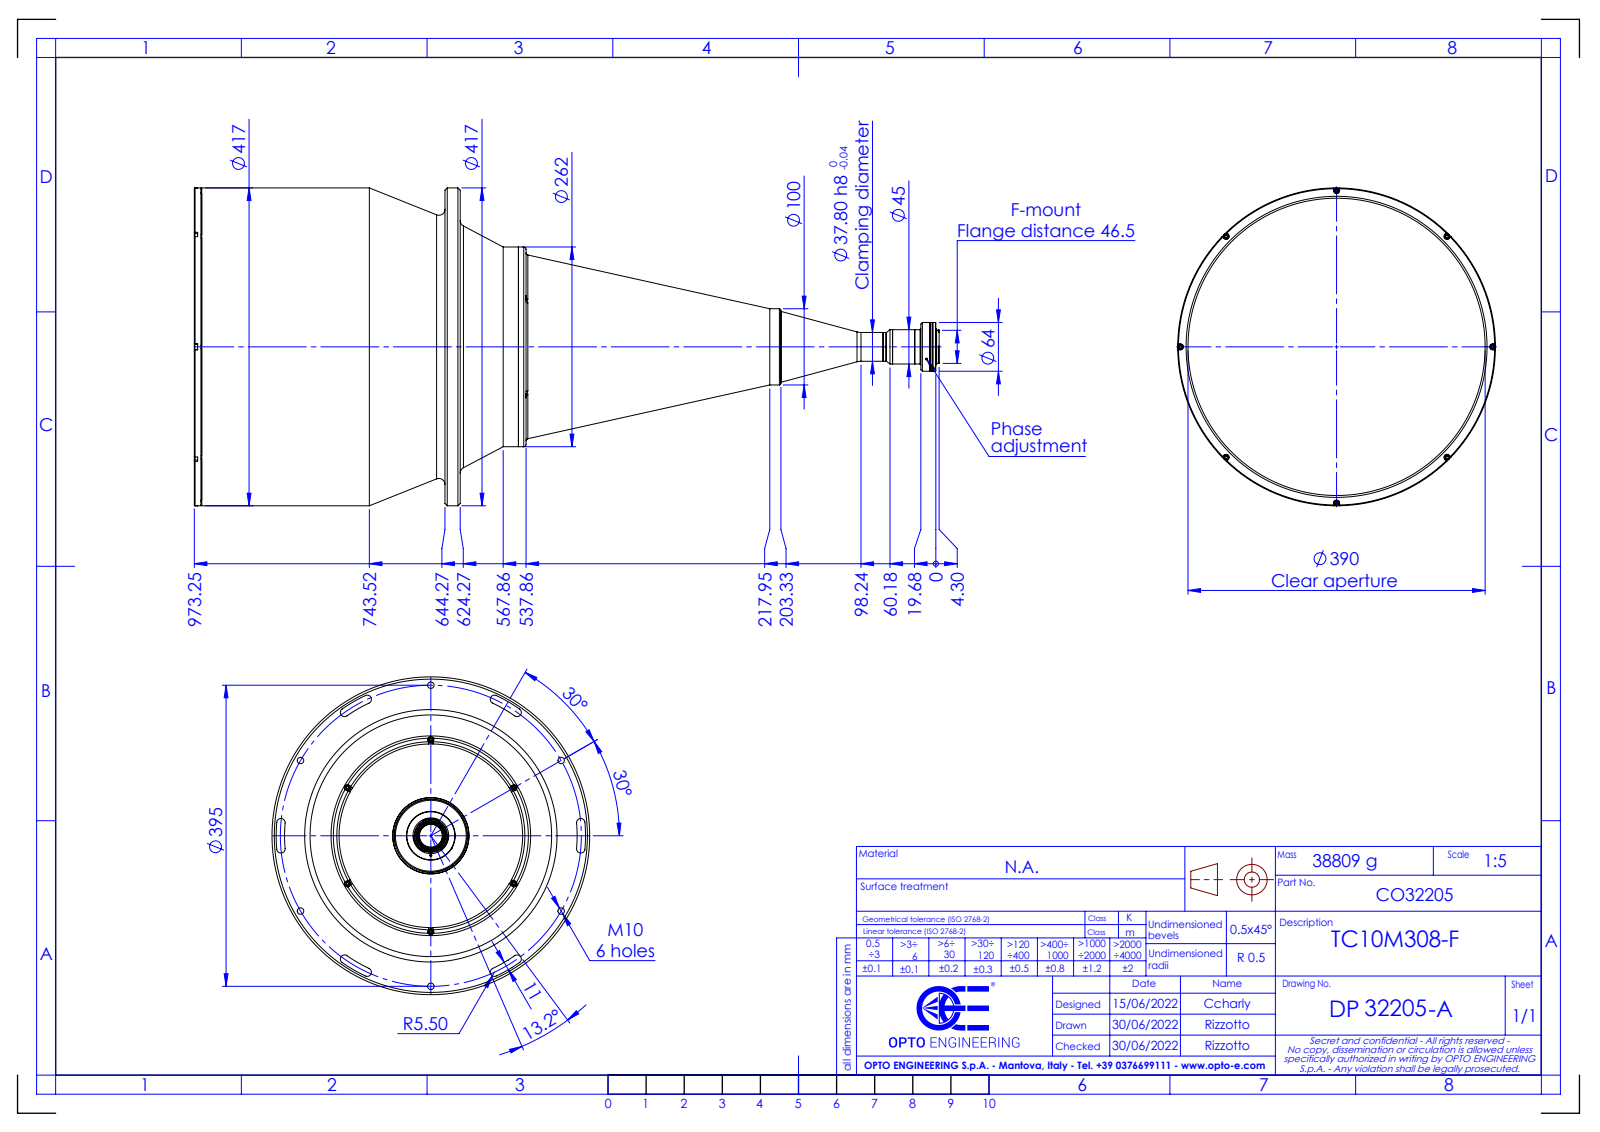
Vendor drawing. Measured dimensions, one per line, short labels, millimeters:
name: DP32205-A_TC10M308-F
written by: SolidWorks 2021 (CONFIG_CONTROL_DESIGN)
unit: mm
bodies: 0 solids, 288 faces (69 planar, 140 cylindrical, 79 other)
size: 977.55 × 417 × 417
holes: 6× ⌀8, 6× ⌀8.5, 3× ⌀2.5, 1× ⌀35, 1× ⌀42, 1× ⌀390
bosses: 8× ⌀7, 1× ⌀417, 1× ⌀262, 1× ⌀100, 1× ⌀64, 1× ⌀63.5, 1× ⌀46.9, 1× ⌀45
rounds: 12× R5.5, 8× R4, 1× R0.5, 1× R22.65, 1× R192, 1× R203
face distances: 20, 328.98, 348.98, 8.7, 320.28, 340.28, 9.73, 1.03, 319.25, 339.25
hole spacings: 126, 173.2, 197.5, 282.43, 71.5, 218.24, 323.5, 342.08
